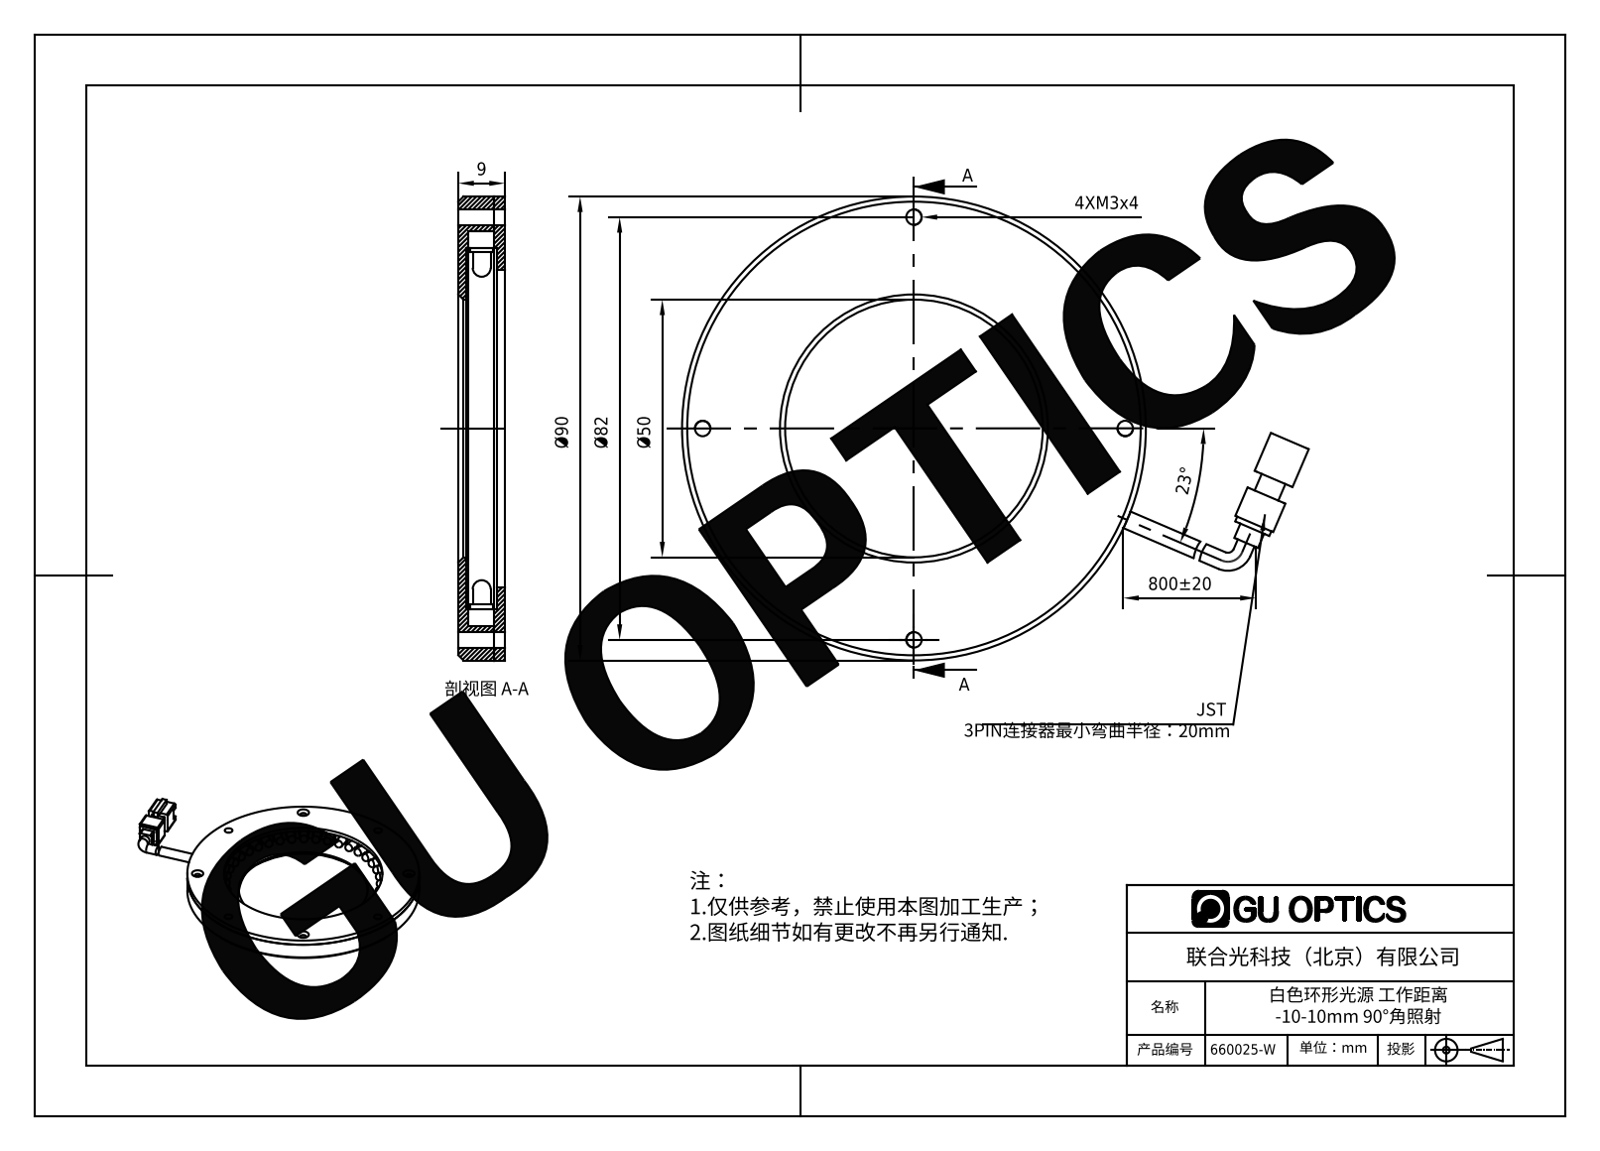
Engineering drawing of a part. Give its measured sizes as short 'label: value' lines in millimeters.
name: 660025-W
written by: SolidWorks 2016 (AUTOMOTIVE_DESIGN)
unit: mm
bodies: 45 solids, 884 faces (553 planar, 267 cylindrical, 64 other)
size: 121.62 × 90 × 10
volume: 25 302 mm³; area: 28 044 mm²
holes: 8× ⌀3, 4× ⌀1.6, 4× ⌀2, 4× ⌀2.4, 2× ⌀3.5, 1× ⌀50, 1× ⌀61.48, 1× ⌀69, 1× ⌀70, 1× ⌀76.68
bosses: 40× ⌀3.8, 40× ⌀3, 2× ⌀3.5, 1× ⌀90, 1× ⌀69.4
rounds: 8× R0.5, 4× R1, 2× R1.8, 1× R5, 1× R33.5, 1× R37.1
face distances: 7, 2, 9, 1.5, 5.5, 7.5, 0.5, 6, 5, 1
hole spacings: 75.76, 82, 31.38, 41, 57.98, 31.35, 31.41, 57.96
